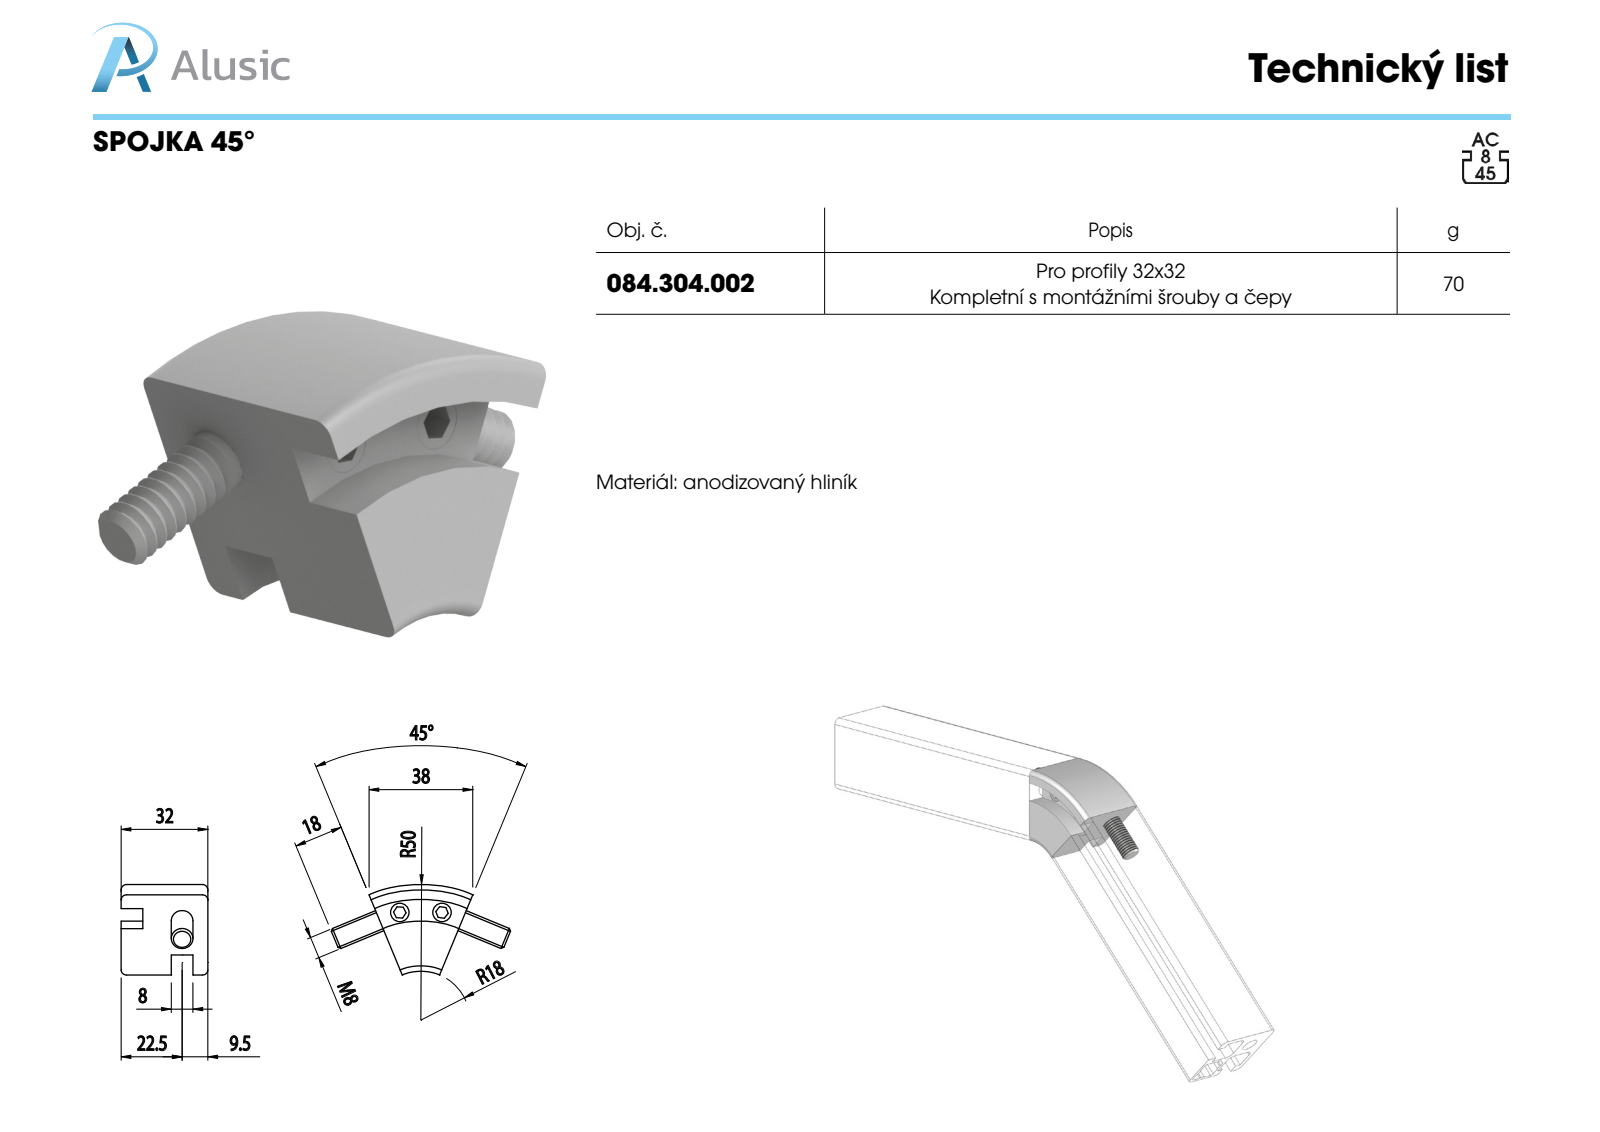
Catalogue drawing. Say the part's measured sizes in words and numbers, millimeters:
The part is named "084.304.002". Its 3-D file was written by "SolidWorks 2011 (CONFIG_CONTROL_DESIGN)". It is 1 solid with 36 faces: 8 planar, 18 cylindrical and 10 other. Overall it measures 38.27 by 33.37 by 32 millimeters. Its volume is 21 792 cubic millimeters and its surface area 7 019 square millimeters. Round holes: 2 of diameter 6.8, 2 of diameter 8. Partial cylindrical surfaces (rounded edges, fillets, slot ends): 1 of radius 18, 1 of radius 26, 1 of radius 36.5, 1 of radius 44.5, 1 of radius 50. The main face-to-face distances are 32, 8, 18.5, 24, 5.5, 26.5, 13.5, 10.5. The hole center spacings are 15.58.
